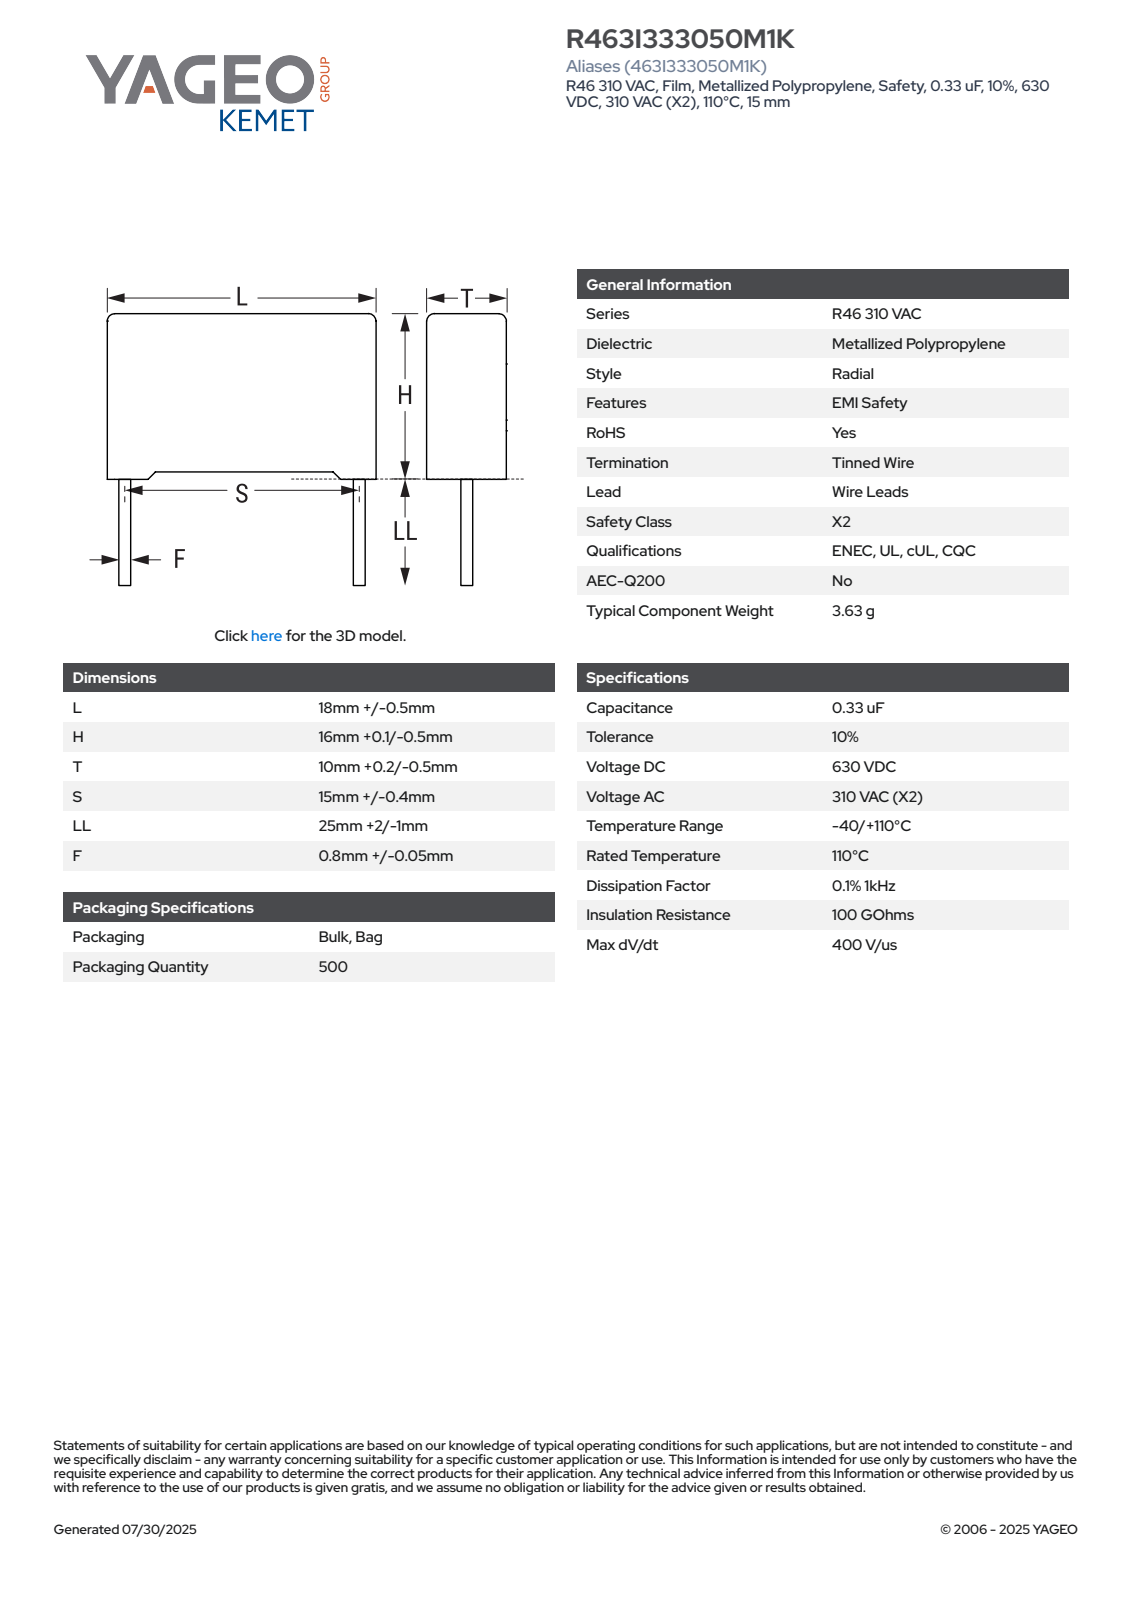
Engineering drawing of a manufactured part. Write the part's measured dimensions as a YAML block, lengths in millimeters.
part_name: "CFR_RB2_18X16X10_L18.5H16.1T10.2S15LL27F0.85"
step_written_by: "SolidWorks 2021 (AUTOMOTIVE_DESIGN)"
units: millimeters
bodies: {solids: 4, faces: 85, planar: 77, cylindrical: 8, other: 0}
overall_size: [43.1, 18.5, 10.21]
volume: 2943
surface_area: 1478
round_bosses_or_shafts:
  - {diameter: 0.85, count: 2}
partial_cylinders:
  - {radius: 0.5, count: 4}
face_to_face_distances: [10.2, 18.5, 15.35, 0.62, 0.75, 16.1, 0.56, 15.54, 17.88, 9.58]
